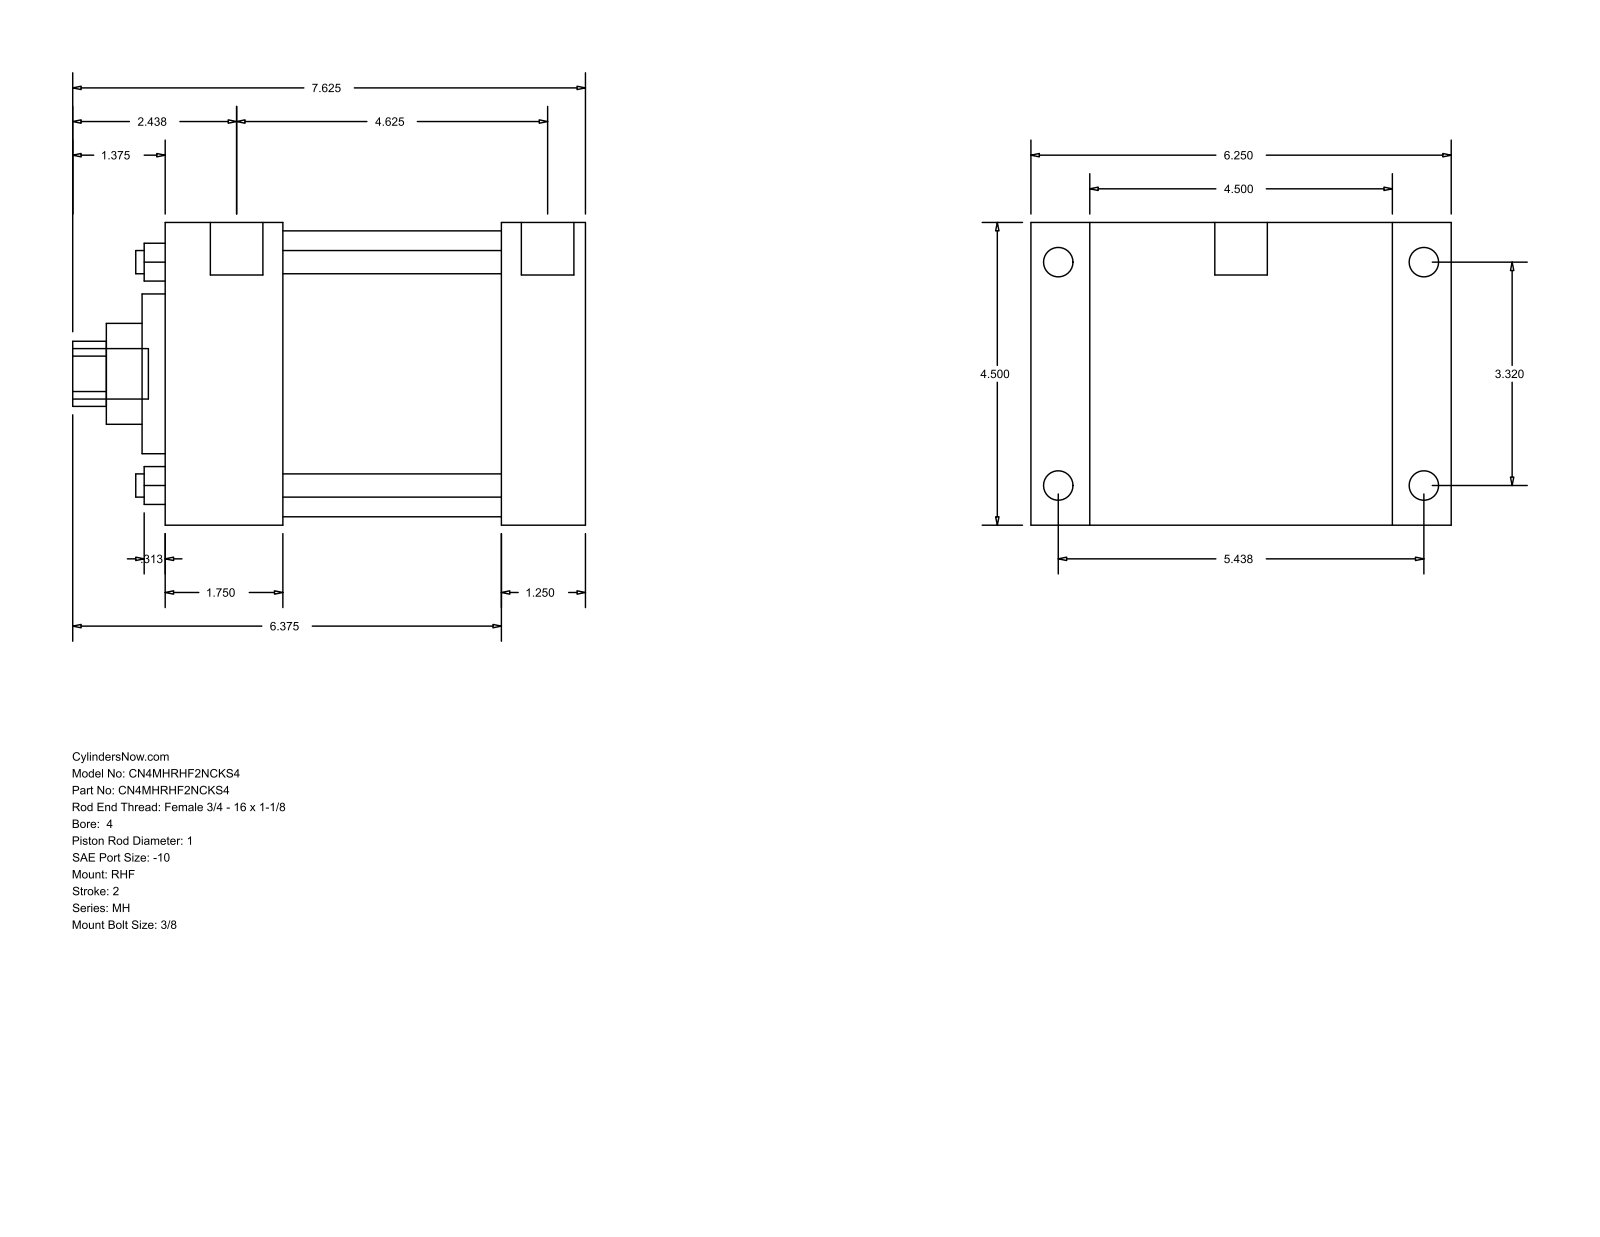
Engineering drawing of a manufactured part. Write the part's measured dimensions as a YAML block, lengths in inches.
part_name: "MH_RHF__0400_1"
step_written_by: "GSSL Pune (CONFIG_CONTROL_DESIGN)"
units: inches
bodies: {solids: 0, faces: 90, planar: 61, cylindrical: 29, other: 0}
overall_size: [7.625, 6.25, 4.5]
round_holes:
  - {diameter: 0.345, count: 4}
  - {diameter: 1, count: 1}
  - {diameter: 1.5, count: 1}
  - {diameter: 2.375, count: 1}
  - {diameter: 4.25, count: 1}
round_bosses_or_shafts:
  - {diameter: 0.438, count: 4}
  - {diameter: 0.344, count: 4}
  - {diameter: 0.781, count: 2}
  - {diameter: 0.75, count: 1}
partial_cylinders:
  - {radius: 0.484, count: 1}
face_to_face_distances: [4.5, 6.25, 5, 1.25, 0.875, 5.375, 1.75, 3.25, 0.344, 2.094]
hole_center_spacings: [2.347, 3.32, 4.695]
